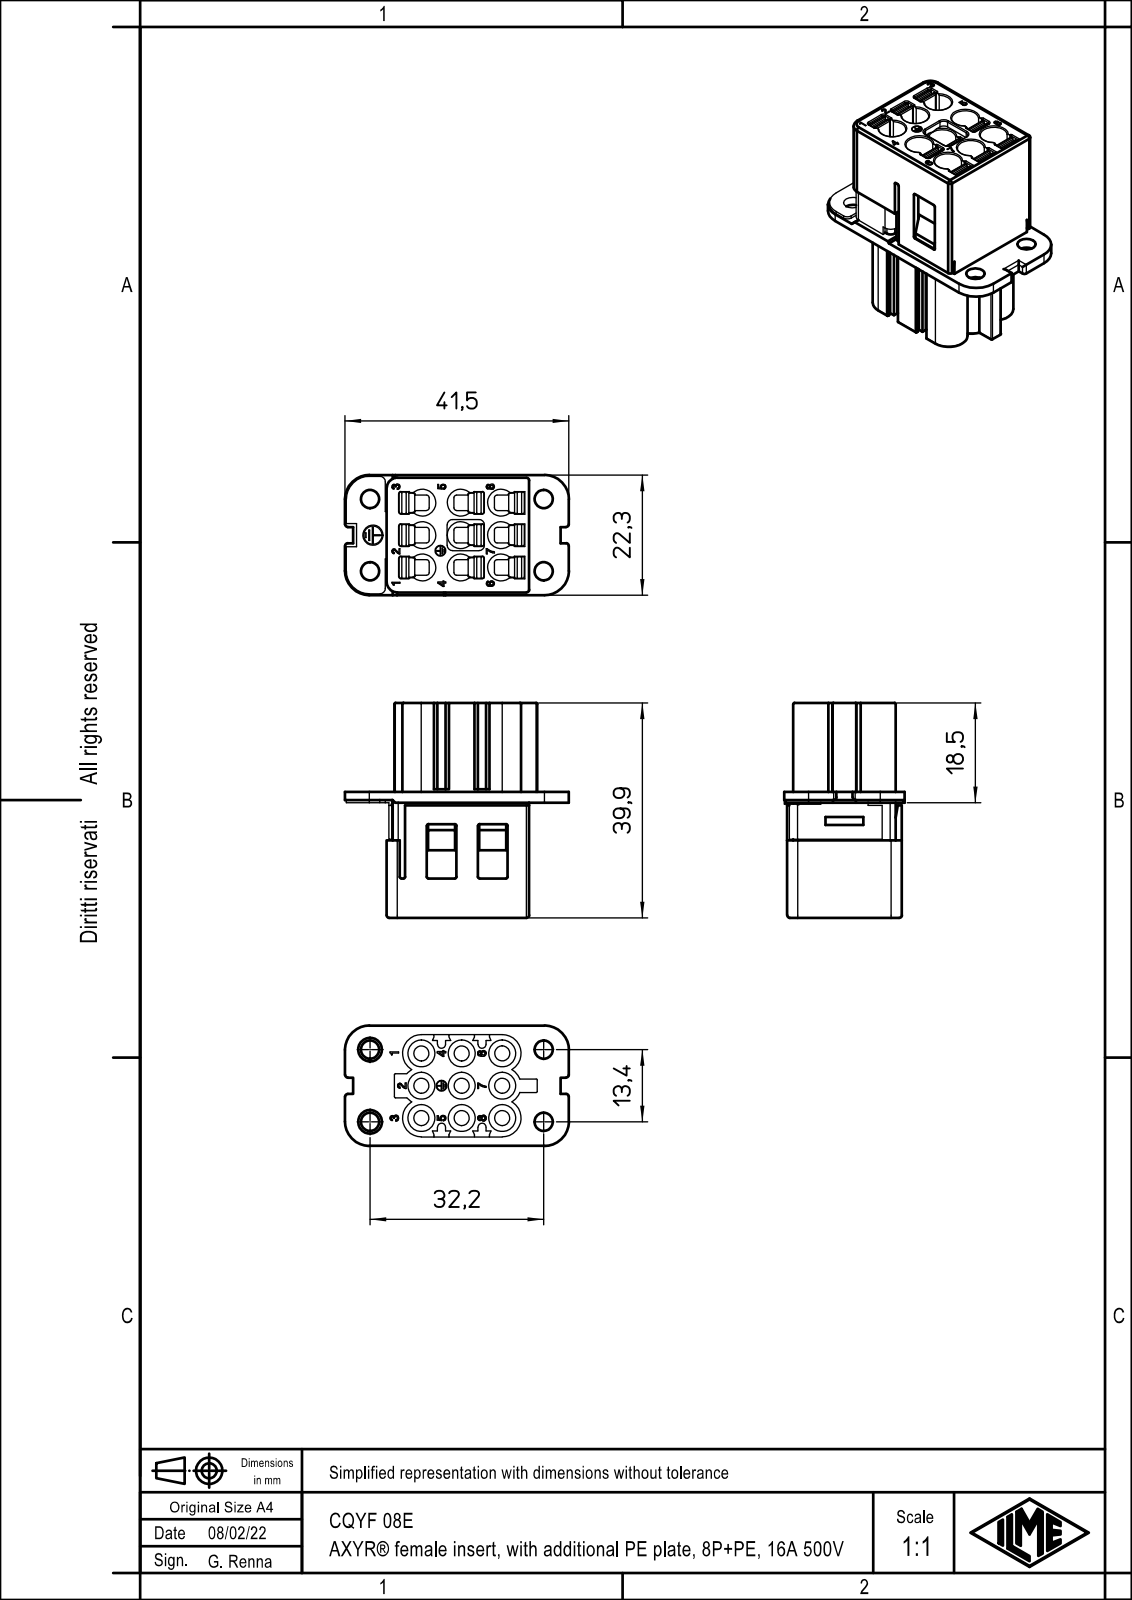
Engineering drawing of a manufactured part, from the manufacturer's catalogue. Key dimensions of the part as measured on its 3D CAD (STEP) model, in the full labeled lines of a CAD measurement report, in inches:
Part name (STEP PRODUCT): CQYF_08E
STEP written by: Creo Elements/Direct Modeling 20.1B 02-Apr-2019 (C) Parametric Technology GmbH (AUTOMOTIVE_DESIGN)
Units: inches
Bodies: 1 solid, 1398 faces (875 planar, 400 cylindrical, 123 other)
Overall size (bounding box): 1.634 × 1.571 × 0.878
Volume: 1.058 in³ · Surface area: 15.88 in²
Round holes (diameter × count): ⌀0.11 ×9, ⌀0.197 ×9, ⌀0.134 ×4, ⌀0.173 ×2, ⌀0.079 ×1
Round bosses / shafts (diameter × count): ⌀0.071 ×1
Partial cylindrical surfaces — rounded edges, fillets, slot ends (radius × count): R0.008 ×71, R0.016 ×48, R0.02 ×36, R0.012 ×29, R0.004 ×18, R0.039 ×15, R0.098 ×9, R0.079 ×6
Main face-to-face distances: 0.045, 0.793, 0.622, 0.02, 0.295, 0.291, 0.079, 0.839, 0.327, 0.331
Hole centre spacings: 0.378, 0.236, 0.295, 0.279, 0.557, 0.585, 0.636, 0.472
